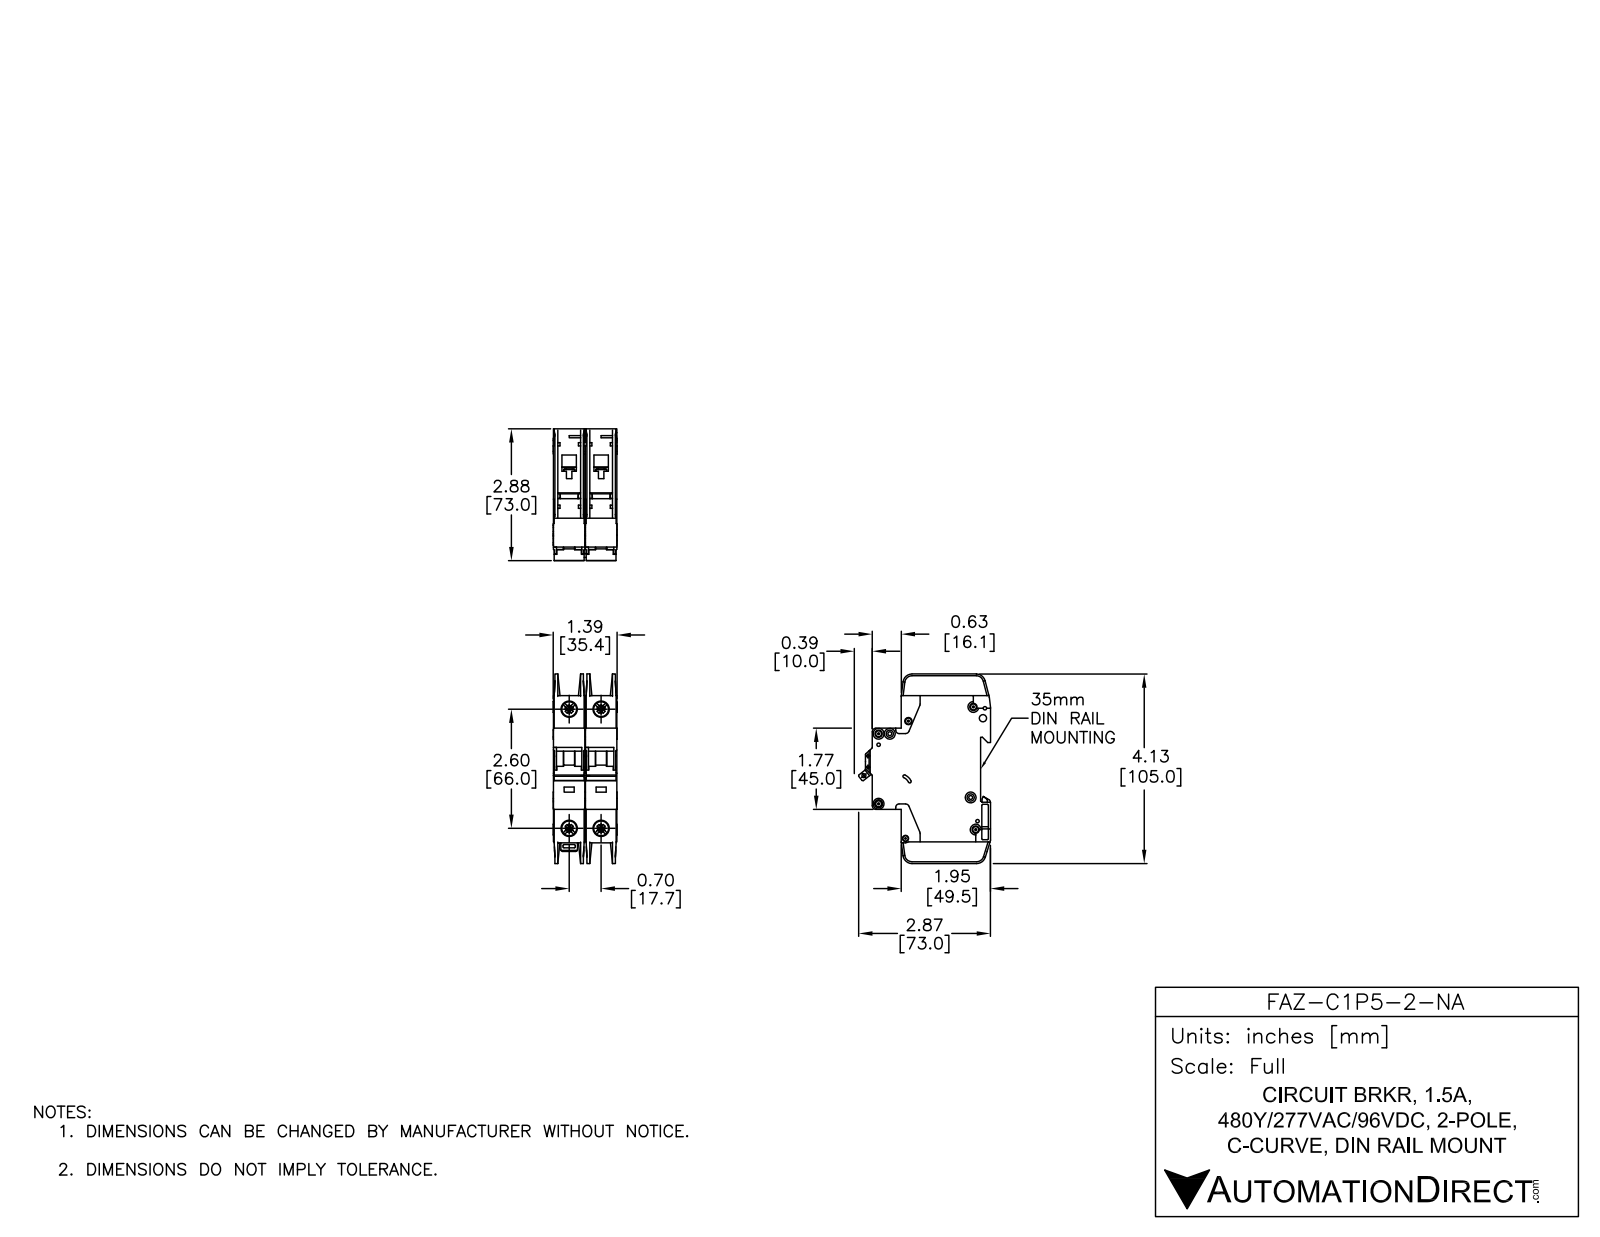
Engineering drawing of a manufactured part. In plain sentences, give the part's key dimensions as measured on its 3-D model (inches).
The part is named "FAZ-C1P5-2-NA". Its 3-D file was written by "SolidWorks 2014 (AUTOMOTIVE_DESIGN)". It is 6 solids with 1568 faces: 818 planar, 526 cylindrical and 224 other. Overall it measures 4.134 by 2.876 by 1.394 inches. Its volume is 9.482 cubic inches and its surface area 76.69 square inches. Round holes: 7 of diameter 0.142, 4 of diameter 0.281, 4 of diameter 0.323, 2 of diameter 0.043, 2 of diameter 0.059, 2 of diameter 0.157, 1 of diameter 0.075, 1 of diameter 0.085, 1 of diameter 0.087, 1 of diameter 0.1, 1 of diameter 0.13, 1 of diameter 0.134. Round bosses or shafts: 7 of diameter 0.236, 2 of diameter 0.098. Partial cylindrical surfaces (rounded edges, fillets, slot ends): 47 of radius 0.01, 24 of radius 0.02, 18 of radius 0.039, 12 of radius 0.079, 5 of radius 0.197, 4 of radius 0.071, 4 of radius 0.157, 2 of radius 0.008. The main face-to-face distances are 0.697, 0.689, 0.028, 0.593, 0.096, 0.069, 0.62, 0.524, 1.386, 0.669. The hole center spacings are 0.244, 0.697, 2.598, 2.69, 0.204, 0.24, 0.322, 0.337.
